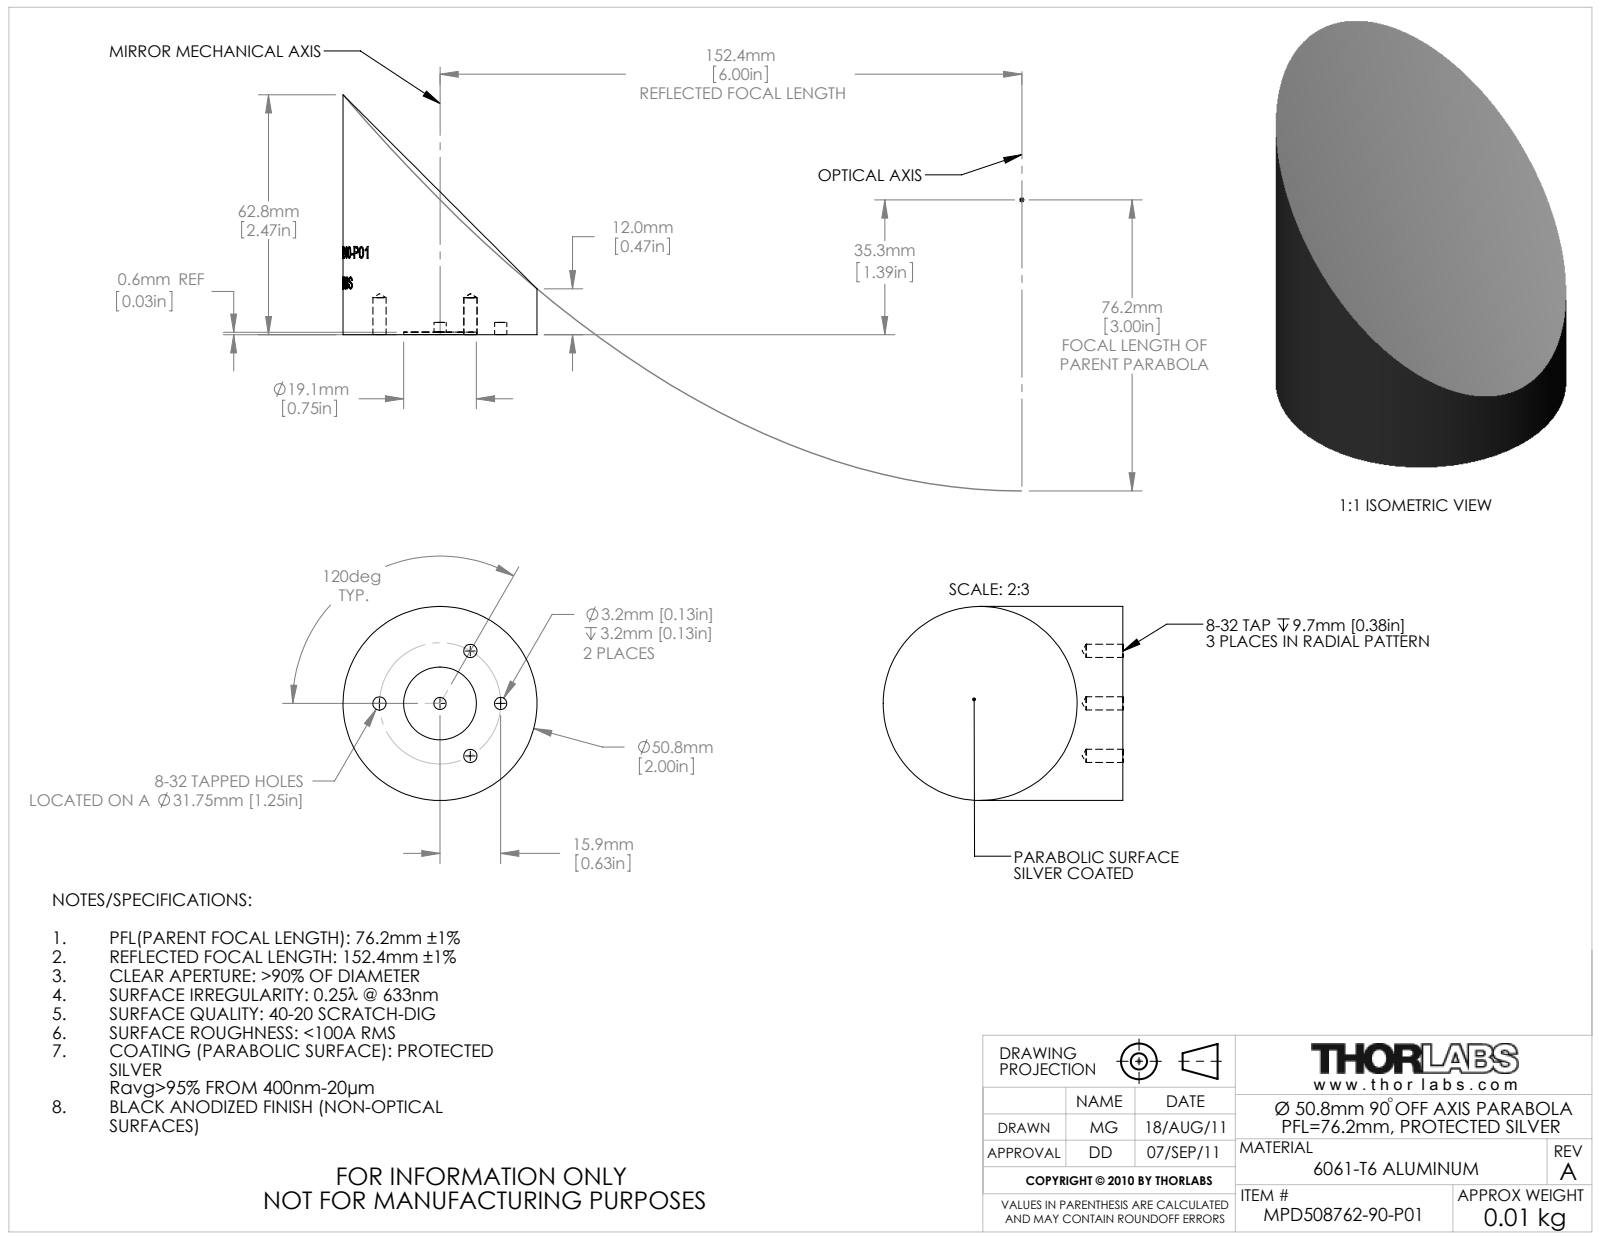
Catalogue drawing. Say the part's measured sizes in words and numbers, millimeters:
The part is named "22881-E0W". Its 3-D file was written by "SolidWorks 2011 (AUTOMOTIVE_DESIGN)". It is 0 solids with 57 faces: 2 planar, 53 cylindrical and 2 other. Overall it measures 62.8 by 50.8 by 50.8 millimeters. Round holes: 3 of diameter 3.45, 2 of diameter 3.19, 1 of diameter 19.05. Round bosses or shafts: 1 of diameter 50.8. The main face-to-face distances are 0.64. The hole center spacings are 15.88, 27.5, 31.76.
